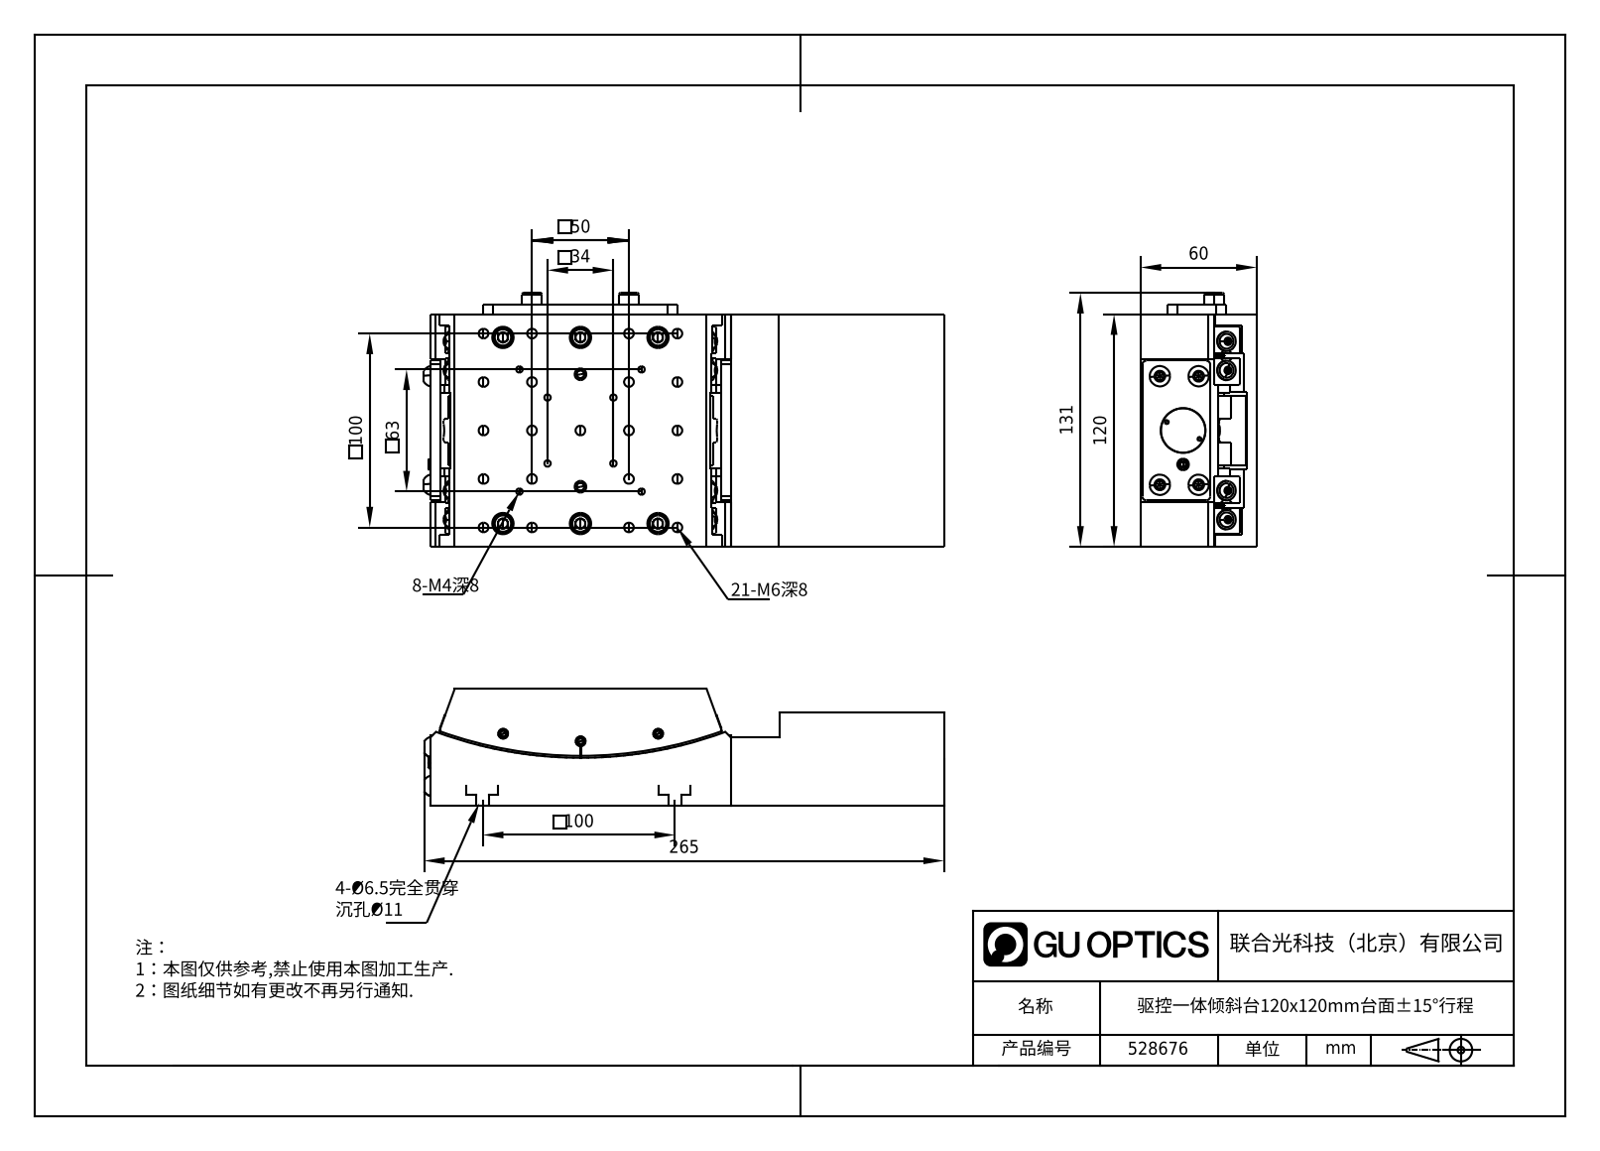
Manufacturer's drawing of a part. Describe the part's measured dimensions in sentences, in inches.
The part is named "528676". Its 3-D file was written by "SolidWorks 2020 (CONFIG_CONTROL_DESIGN)". It is 104 solids with 2984 faces: 1368 planar, 768 cylindrical and 848 other. Overall it measures 10.563 by 5.157 by 2.362 inches. Its volume is 89.7 cubic inches and its surface area 465.6 square inches. Round holes: 56 of diameter 0.197, 28 of diameter 0.13, 12 of diameter 0.374, 10 of diameter 0.256, 10 of diameter 0.433, 8 of diameter 0.217, 6 of diameter 0.165, 6 of diameter 0.244, 6 of diameter 0.315, 4 of diameter 0.059, 4 of diameter 0.063, 4 of diameter 0.081. Round bosses or shafts: 20 of diameter 0.157, 17 of diameter 0.236, 16 of diameter 0.394, 10 of diameter 0.276, 6 of diameter 0.335, 6 of diameter 0.197, 2 of diameter 0.098, 1 of diameter 1.024. Partial cylindrical surfaces (rounded edges, fillets, slot ends): 24 of radius 0.012, 10 of radius 0.138, 8 of radius 0.197, 4 of radius 0.079, 4 of radius 0.098, 4 of radius 0.118, 2 of radius 0.089, 1 of radius 5.394. The main face-to-face distances are 4.724, 2.363, 0.197, 0.473, 1.89, 5.906, 1.594, 3.13, 0.157, 3.031. The hole center spacings are 3.031, 0.748, 3.416, 1.575, 2.283, 2.774, 3.681, 0.63.
